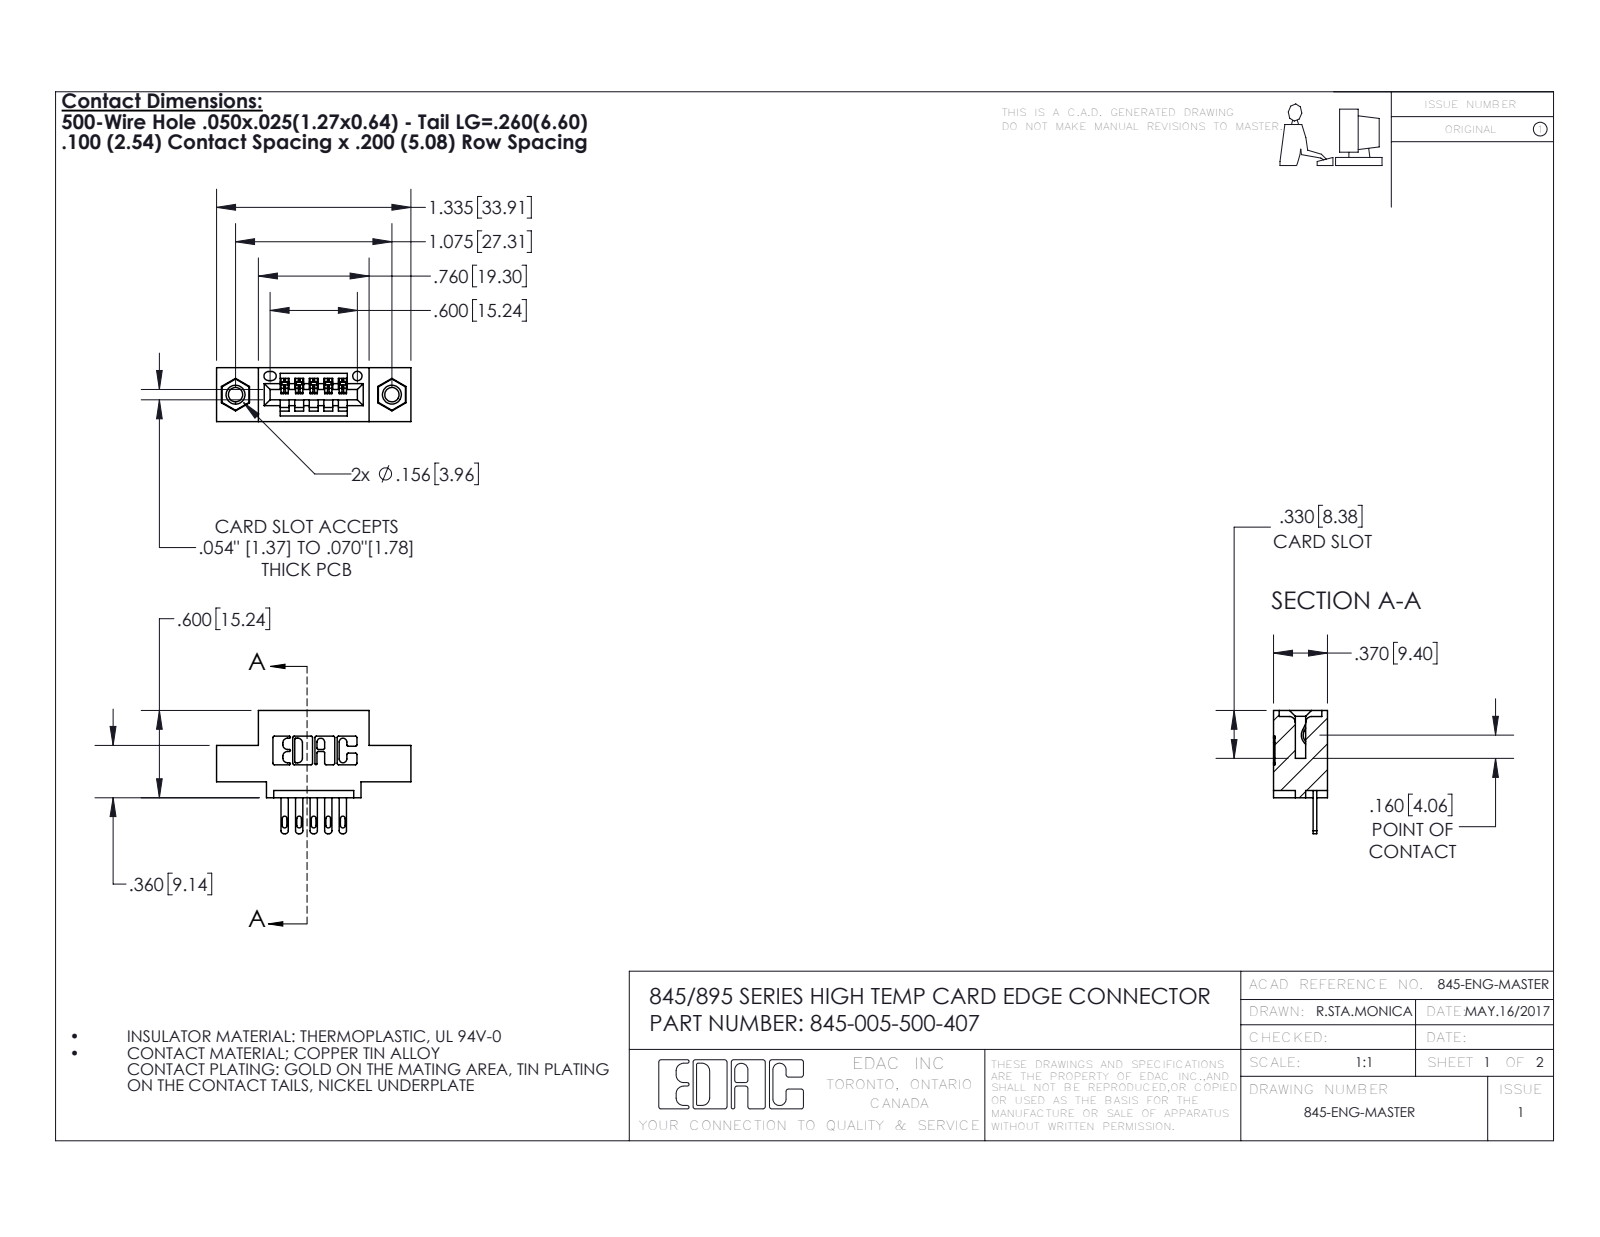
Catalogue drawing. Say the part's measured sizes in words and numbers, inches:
The part is named "345-292-001_345-293-100; 345-005-500-407; 345-250-001_345-250-005-103; 345 Part_0.110 Offset - 0.156 Dia-TI". Its 3-D file was written by "SolidWorks 2016 (CONFIG_CONTROL_DESIGN)". It is 8 solids with 460 faces: 286 planar, 158 cylindrical and 16 other. Overall it measures 1.335 by 0.847 by 0.37 inches. Its volume is 0.173 cubic inches and its surface area 5.253 square inches. Round holes: 2 of diameter 0.098, 2 of diameter 0.125, 2 of diameter 0.156, 1 of diameter 0.064. Round bosses or shafts: 2 of diameter 0.155. Partial cylindrical surfaces (rounded edges, fillets, slot ends): 22 of radius 0.01, 10 of radius 0.006, 10 of radius 0.016, 10 of radius 0.02, 6 of radius 0.007, 6 of radius 0.031, 3 of radius 0.026, 2 of radius 0.031. The main face-to-face distances are 0.2, 0.37, 0.072, 0.298, 0.1, 0.025, 0.098, 0.272, 0.25, 0.06. The hole center spacings are 0.27, 0.847, 1.075.
